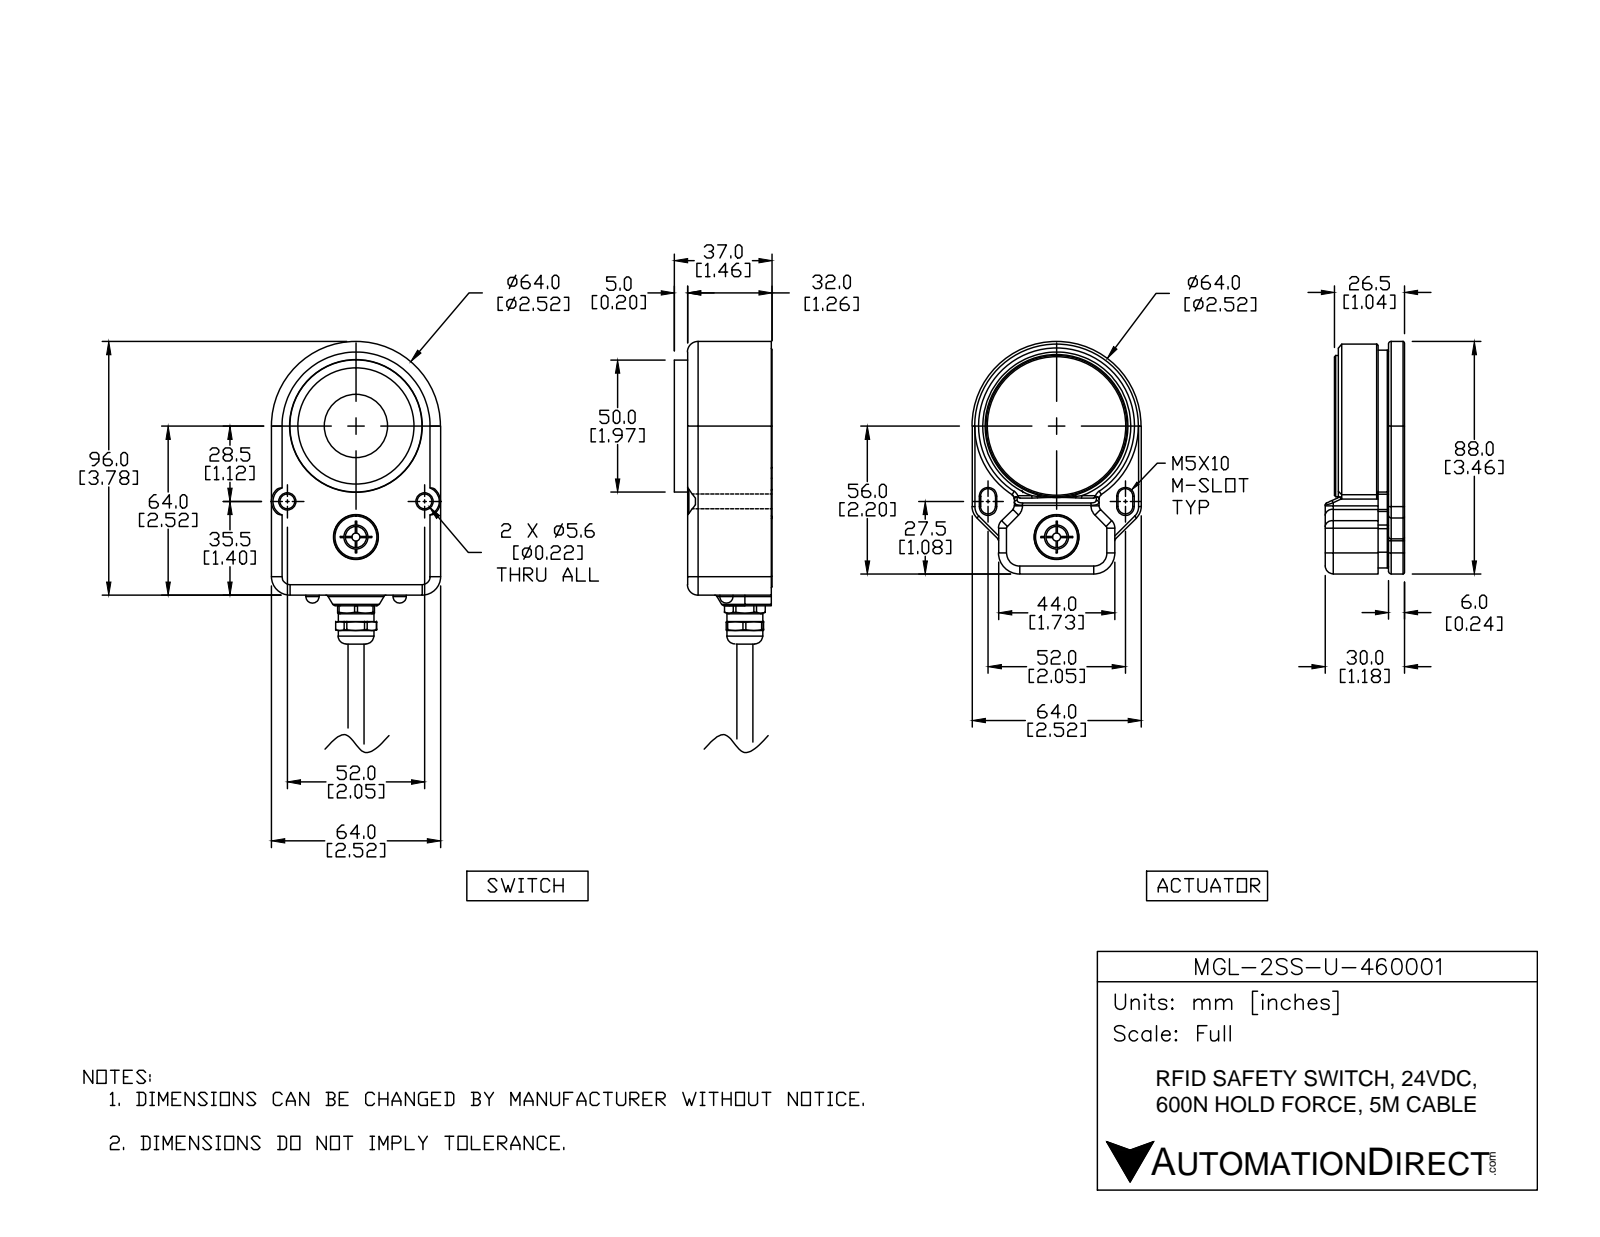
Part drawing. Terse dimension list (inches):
name: MGL-2SS-U-460001; MGL-2SS-U-460001_1; MGL-2SS-U-460001_2
written by: SolidWorks 2017 (AUTOMOTIVE_DESIGN)
unit: in
bodies: 20 solids, 1740 faces (445 planar, 724 cylindrical, 571 other)
size: 7.717 × 2.539 × 2.52
volume: 12.53 in³; area: 169.9 in²
holes: 8× ⌀0.098, 8× ⌀0.157, 6× ⌀0.13, 6× ⌀0.315, 5× ⌀0.197, 3× ⌀0.354, 2× ⌀0.22, 2× ⌀0.413, 2× ⌀0.669, 1× ⌀0.252, 1× ⌀0.264, 1× ⌀0.268
bosses: 4× ⌀0.02, 2× ⌀0.236, 2× ⌀0.228, 2× ⌀0.22, 2× ⌀0.118, 1× ⌀2.441, 1× ⌀2.26, 1× ⌀2.102
rounds: 218× R0.02, 69× R0.039, 30× R0.079, 17× R0.012, 15× R0.118, 12× R0.157, 8× R0.236, 7× R0.024
face distances: 0.098, 0.236, 0.413, 0.118, 1.89, 0.748, 1.043, 0.394, 1.142, 0.079
hole spacings: 0.706, 0.768, 1.086, 1.024, 2.147, 0.346, 0.376, 0.382
